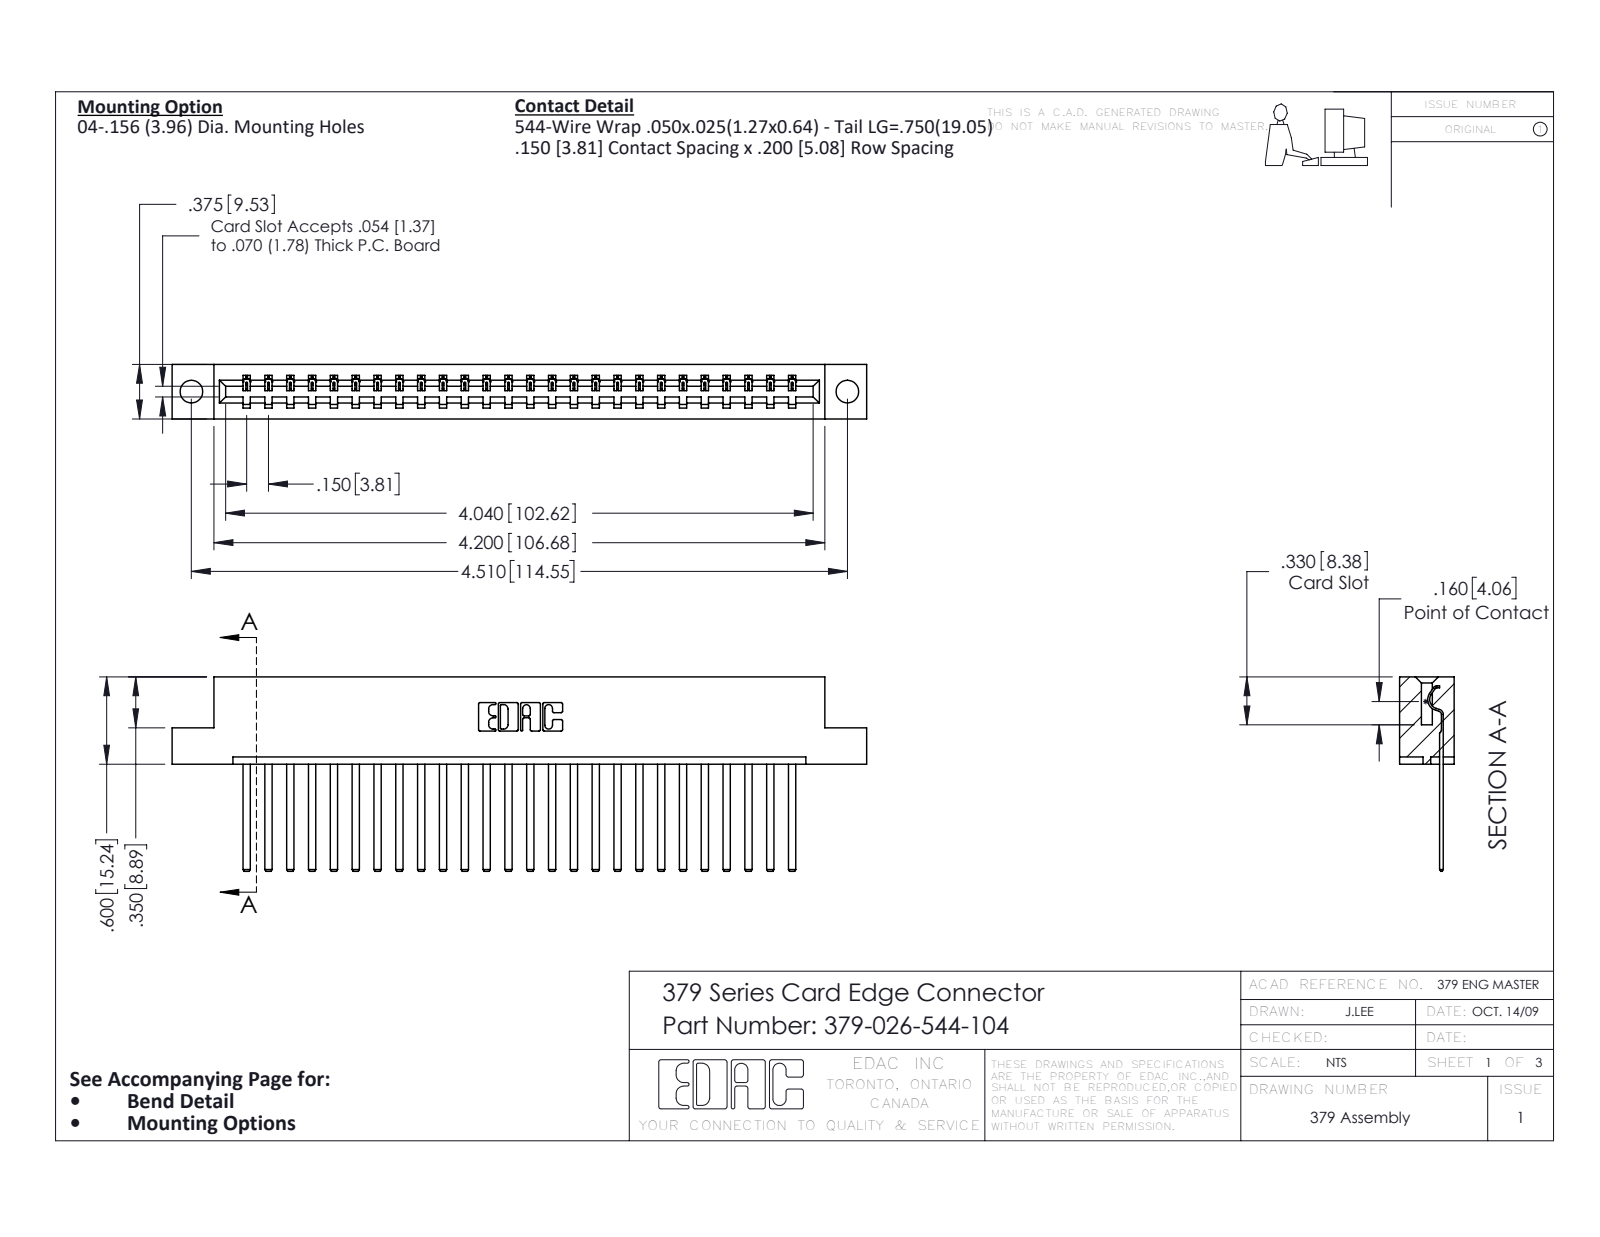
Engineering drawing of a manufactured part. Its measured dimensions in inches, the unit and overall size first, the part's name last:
Units: inches
Overall size (bounding box): 4.775 × 1.337 × 0.375
Round holes (diameter × count): ⌀0.156 ×2
Partial cylindrical surfaces — rounded edges, fillets, slot ends (radius × count): R0.006 ×52, R0.01 ×22, R0.007 ×6, R0.031 ×6, R0.026 ×3, R0.014 ×1, R0.022 ×1, R0.024 ×1
Main face-to-face distances: 0.3, 0.075, 0.375, 0.275, 0.1, 0.025, 0.6, 0.225, 0.15, 0.2
Hole centre spacings: 4.51
Volume: 0.779 in³ · Surface area: 21.34 in²
Bodies: 27 solids, 1466 faces (1058 planar, 408 cylindrical, 0 other)
Part name (STEP PRODUCT): 345-292-001_345-293-144; 379-026-544-104; 379 Part_Flush - .156 Dia - TH
STEP written by: SolidWorks 2016 (CONFIG_CONTROL_DESIGN)
